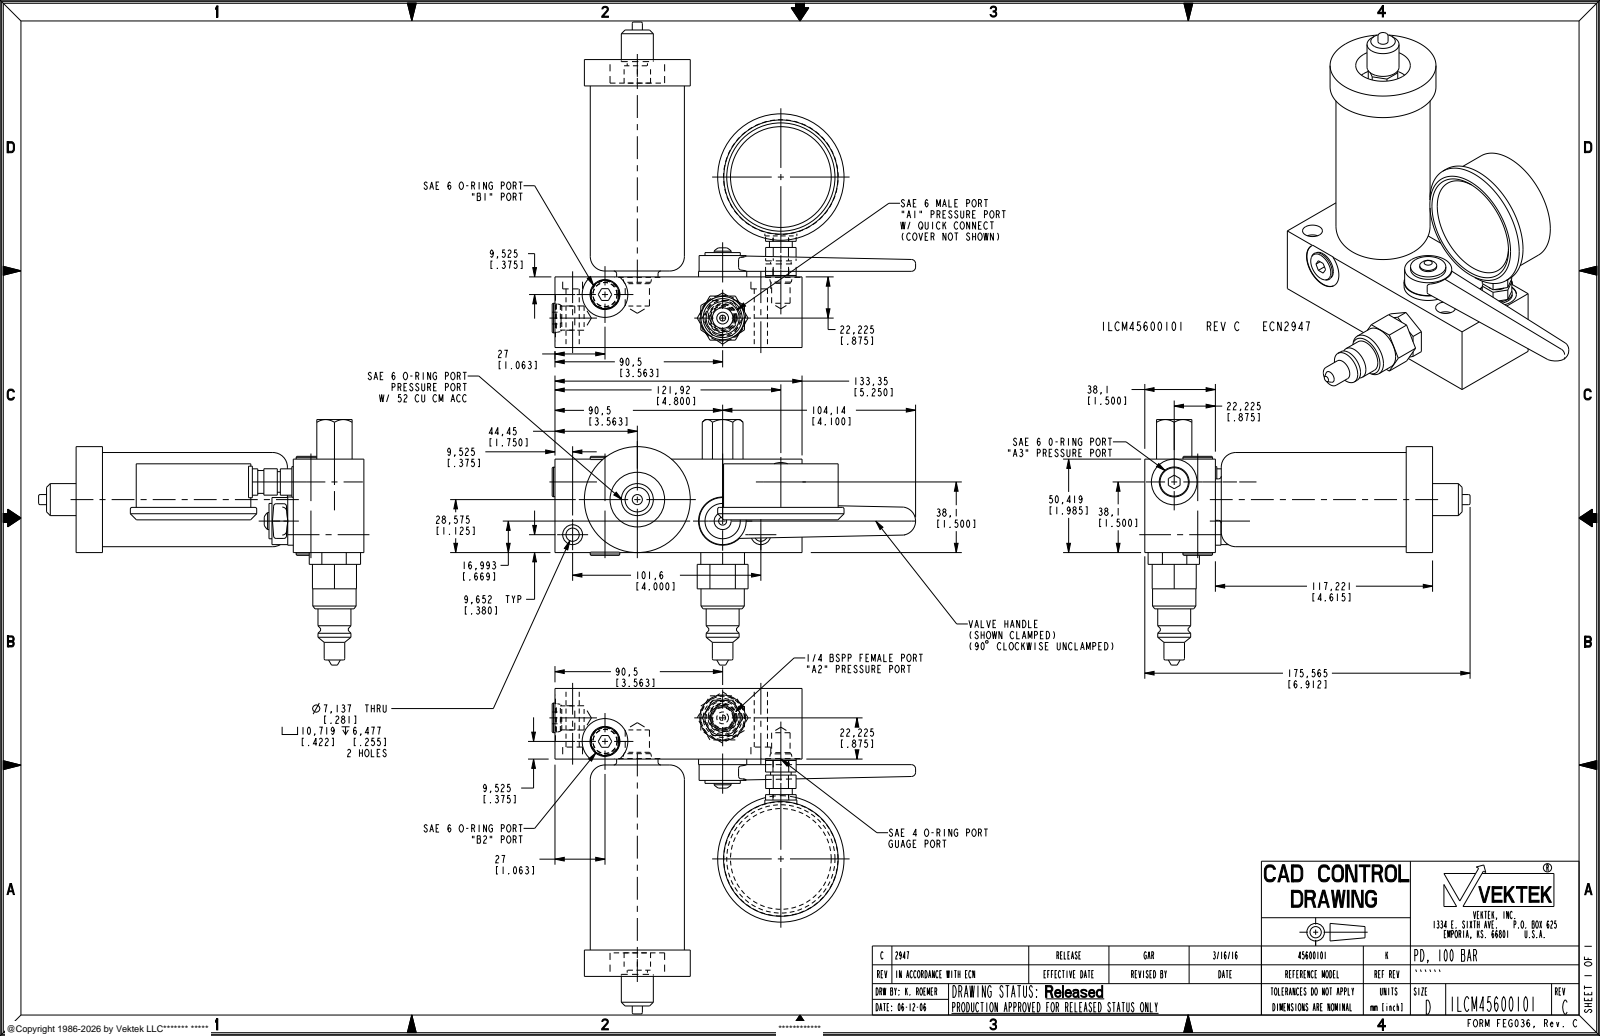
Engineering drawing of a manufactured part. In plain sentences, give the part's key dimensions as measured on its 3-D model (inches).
The part is named "ILCM45600101". Its 3-D file was written by "PRO/ENGINEER BY PARAMETRIC TECHNOLOGY CORPORATION, 2013320 (AUTOMOTIVE_DESIGN)". It is 5 solids with 342 faces: 145 planar, 93 cylindrical and 104 other. Overall it measures 7.722 by 6.912 by 5.214 inches. Its volume is 37.35 cubic inches and its surface area 139.1 square inches. Round holes: 4 of diameter 0.515, 3 of diameter 0.97, 2 of diameter 0.281, 2 of diameter 0.422, 1 of diameter 0.392, 1 of diameter 0.468, 1 of diameter 0.825, 1 of diameter 1.16. Round bosses or shafts: 4 of diameter 0.563, 2 of diameter 0.51, 1 of diameter 2.685, 1 of diameter 2.435, 1 of diameter 2.25, 1 of diameter 2, 1 of diameter 1.024, 1 of diameter 1. Partial cylindrical surfaces (rounded edges, fillets, slot ends): 2 of radius 0.09, 1 of radius 0.3, 1 of radius 0.485. The main face-to-face distances are 1.5, 1.985, 0.1, 1.885, 0.775, 1.21, 1.11, 4.615, 6.115, 5.25. The hole center spacings are 1.198, 1.564, 2.55, 2.729, 3.073, 4, 4.564.
